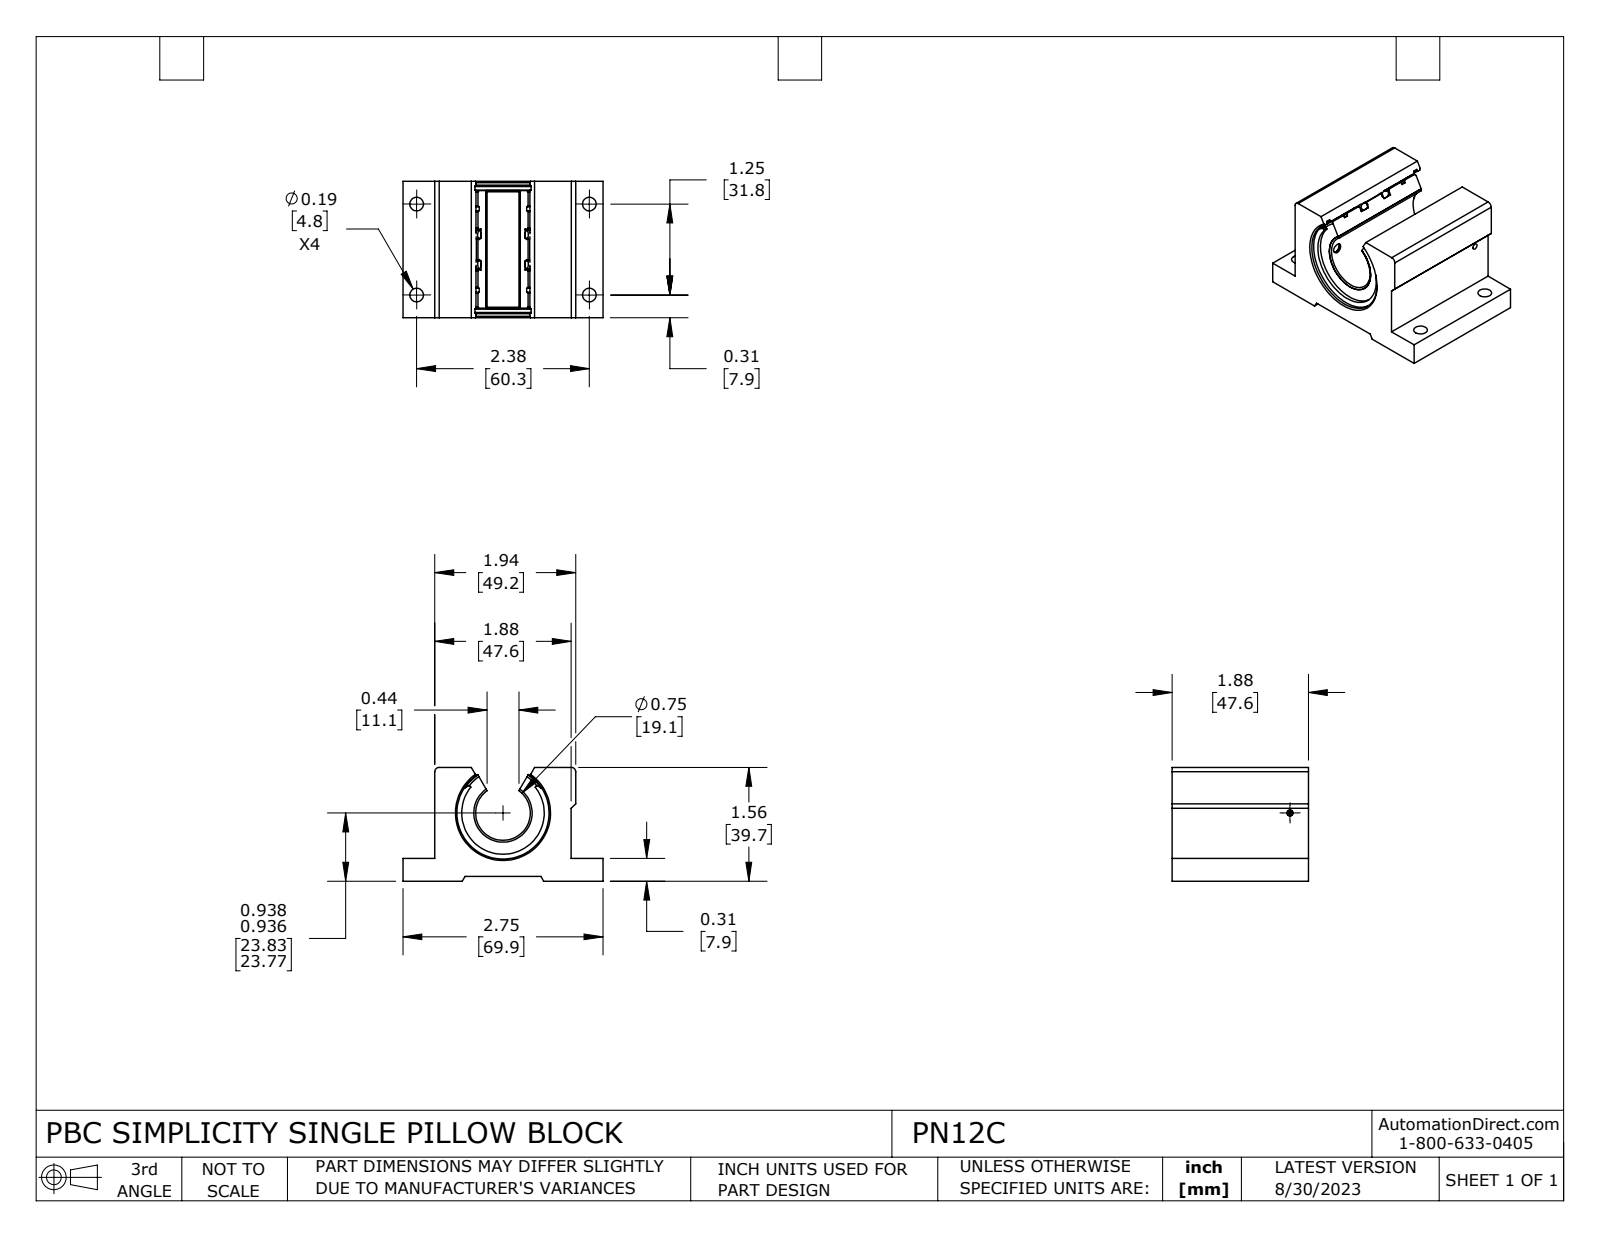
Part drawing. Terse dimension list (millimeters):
name: PN12C
written by: SolidWorks 2021 (CONFIG_CONTROL_DESIGN)
unit: mm
bodies: 8 solids, 206 faces (53 planar, 94 cylindrical, 59 other)
size: 69.9 × 47.6 × 39.7
volume: 73 760 mm³; area: 30 800 mm²
holes: 4× ⌀4.7, 1× ⌀1.4, 1× ⌀2, 1× ⌀3.5, 1× ⌀19.1, 1× ⌀20.4, 1× ⌀32.2, 1× ⌀33.8
bosses: 1× ⌀31.7, 1× ⌀29.9, 1× ⌀27.6, 1× ⌀2
rounds: 2× R0.8, 2× R1.5, 2× R4.6, 1× R14.4, 1× R17.2
face distances: 47.6, 1.7, 39.7, 38, 7.9, 6.3, 31.8, 11.1, 58.7, 3.3
hole spacings: 31.8, 60.3, 68.2, 34.7
